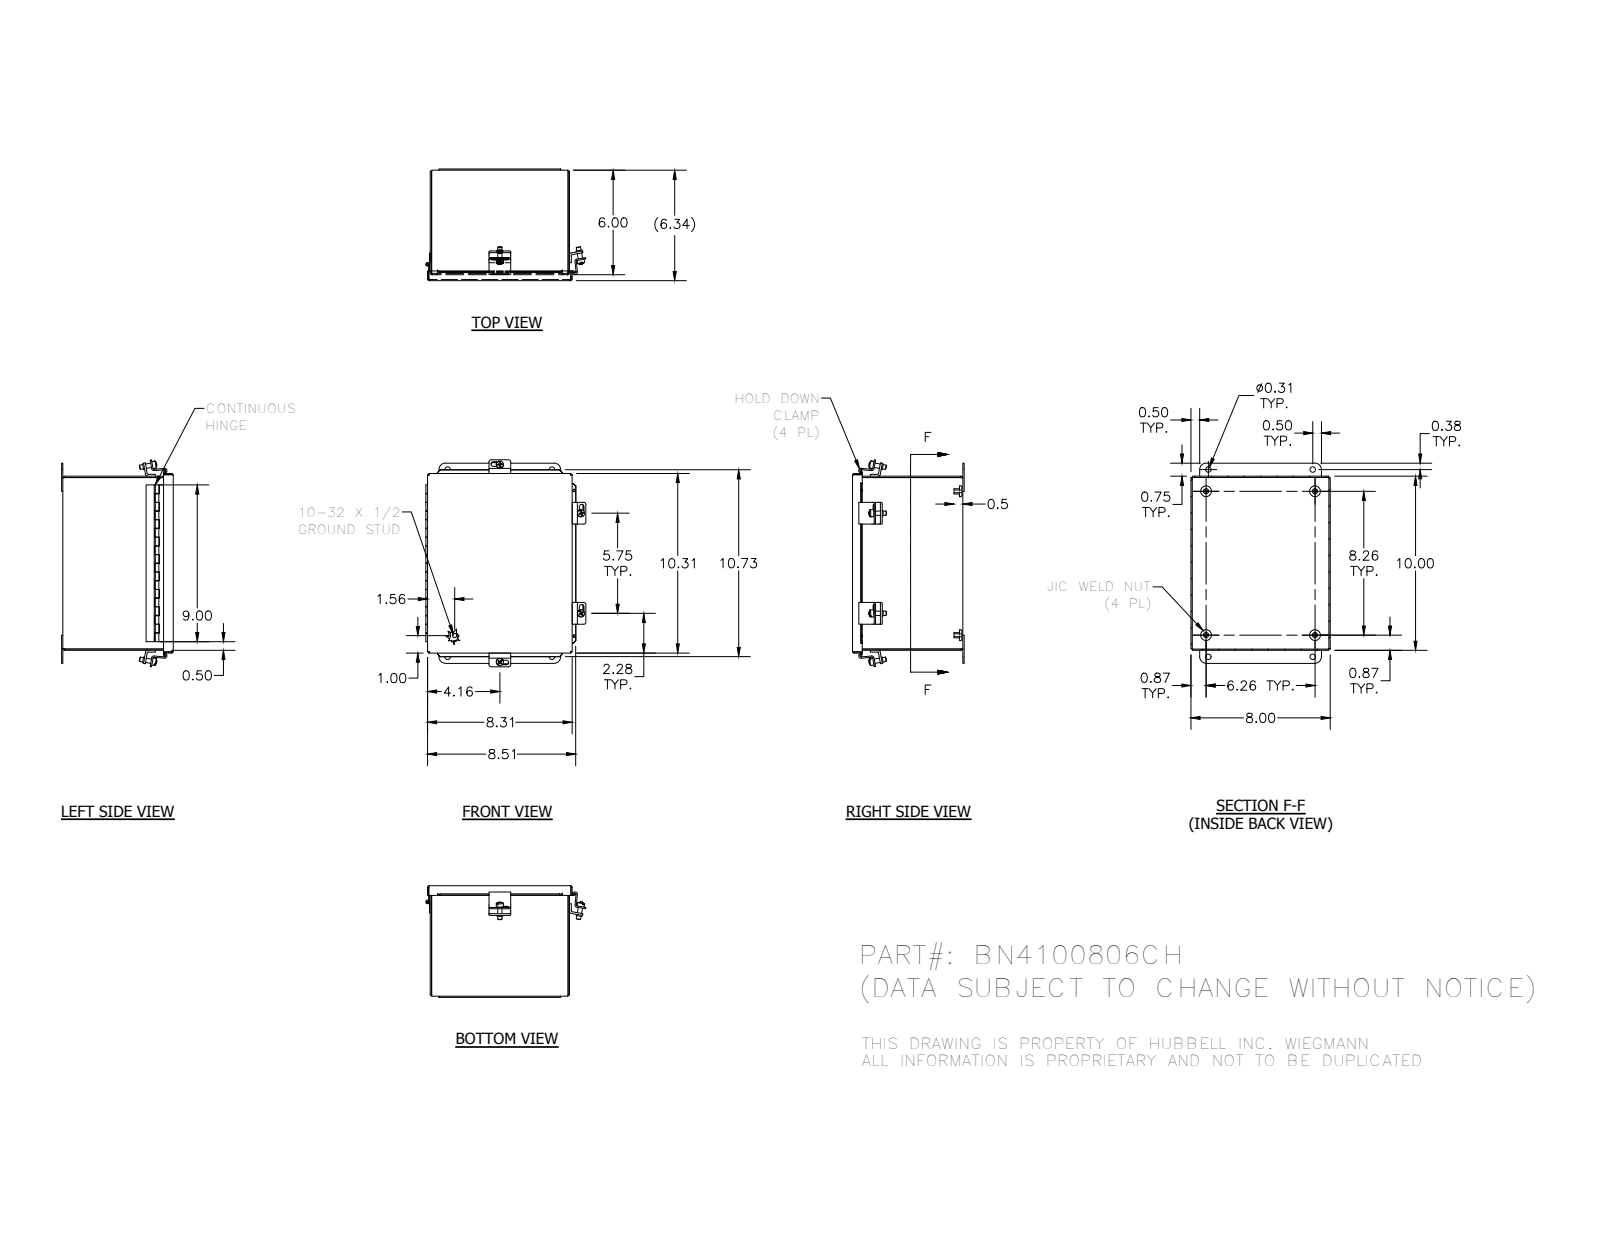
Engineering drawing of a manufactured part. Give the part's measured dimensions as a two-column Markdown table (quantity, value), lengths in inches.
| quantity | value |
| --- | --- |
| part name | B_1008CH_LID; 316164; 38811; 3499 (+8 more) |
| STEP written by | Autodesk Inventor 2016 (AUTOMOTIVE_DESIGN) |
| units | inches |
| bodies | 20 solids, 487 faces (313 planar, 123 cylindrical, 51 other) |
| overall size | 11.5 × 9.086 × 6.259 |
| volume | 35.77 in³ |
| surface area | 984.4 in² |
| round holes (diameter × count) | 0.156 × 4, 0.31 × 4, 0.14 × 2, 0.196 × 2, 0.117 × 1 |
| round bosses / shafts (diameter × count) | 0.625 × 4, 0.3 × 4, 0.25 × 3, 0.409 × 2, 0.344 × 2, 0.2 × 1, 0.19 × 1, 0.1 × 1 |
| partial cylindrical surfaces (radius × count) | 0.047 × 8, 0.121 × 8, 0.125 × 8, 0.078 × 4, 0.133 × 4, 0.137 × 4, 0.375 × 4, 0.031 × 3 |
| main face-to-face distances | 0.074, 7.926, 6.125, 0.059, 9.926, 6.184, 6.051, 6.11, 8, 7.852 |
| hole center spacings | 1.256, 9.501, 6, 6.25, 6.251, 6.252, 8.25, 10.35 |
